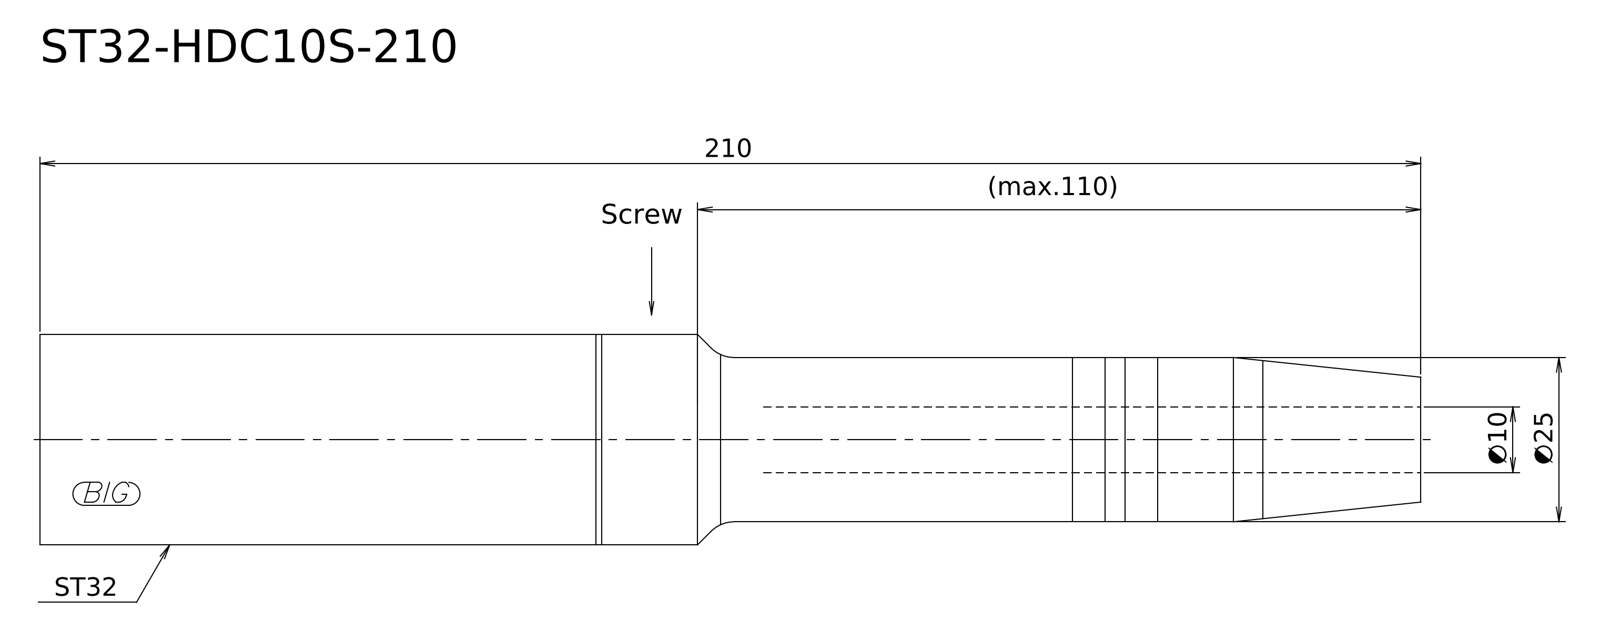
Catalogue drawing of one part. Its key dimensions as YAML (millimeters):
step_written_by: "Kubotek KeyCreator V8.5.1 (14335) (CONFIG_CONTROL_DESIGN)"
units: millimeters
bodies: {solids: 1, faces: 7, planar: 2, cylindrical: 2, other: 3}
overall_size: [210, 32, 32]
volume: 131977
surface_area: 19674
round_bosses_or_shafts:
  - {diameter: 32, count: 1}
  - {diameter: 25, count: 1}
face_to_face_distances: [210]
